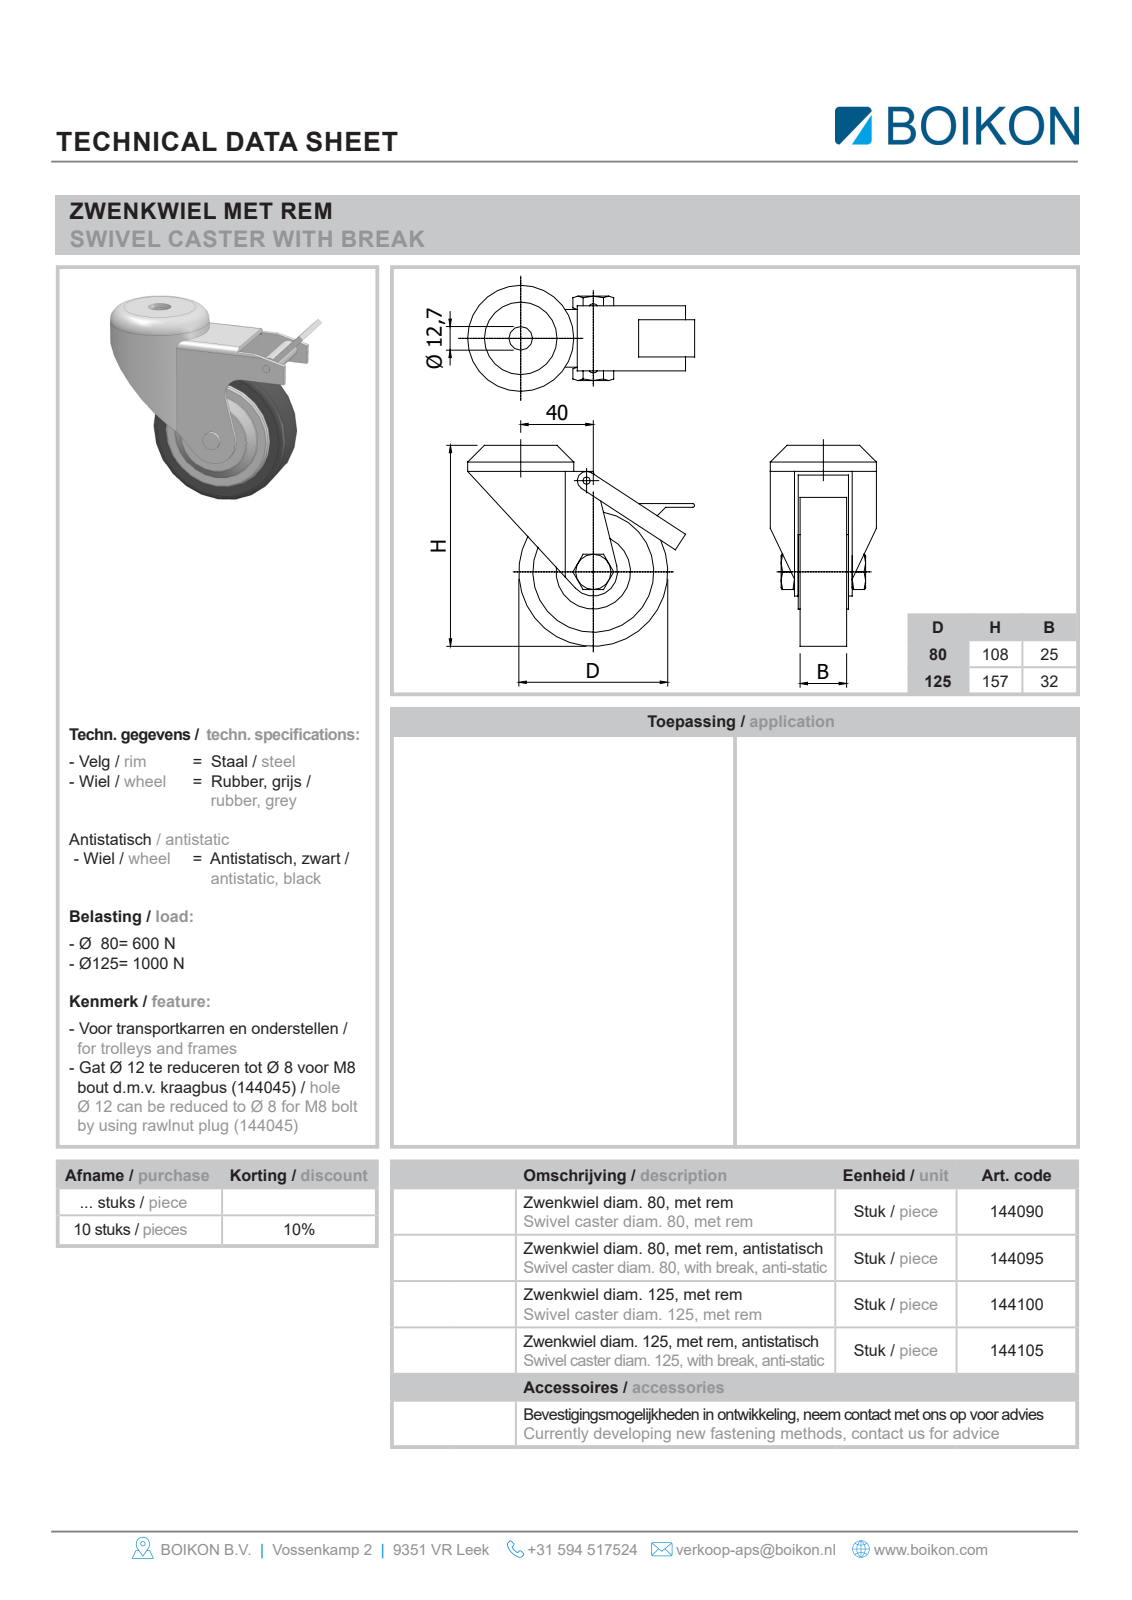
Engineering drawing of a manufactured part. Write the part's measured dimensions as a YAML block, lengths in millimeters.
part_name: "Root; 144100Zwenkwiel diam. 125, met remBOIKON"
step_written_by: "HiCAD 2013 1802.4 Build 509 (AUTOMOTIVE_DESIGN)"
units: millimeters
bodies: {solids: 1, faces: 48, planar: 23, cylindrical: 21, other: 4}
overall_size: [158, 131, 59]
volume: 444542
surface_area: 70002
round_holes:
  - {diameter: 12.5, count: 1}
round_bosses_or_shafts:
  - {diameter: 125, count: 1}
  - {diameter: 57, count: 1}
  - {diameter: 10, count: 1}
  - {diameter: 4, count: 1}
partial_cylinders:
  - {radius: 5, count: 5}
  - {radius: 8, count: 1}
  - {radius: 26.5, count: 1}
face_to_face_distances: [3, 32, 6.5, 38.5, 9.5, 41.5, 48, 45, 6, 51]
